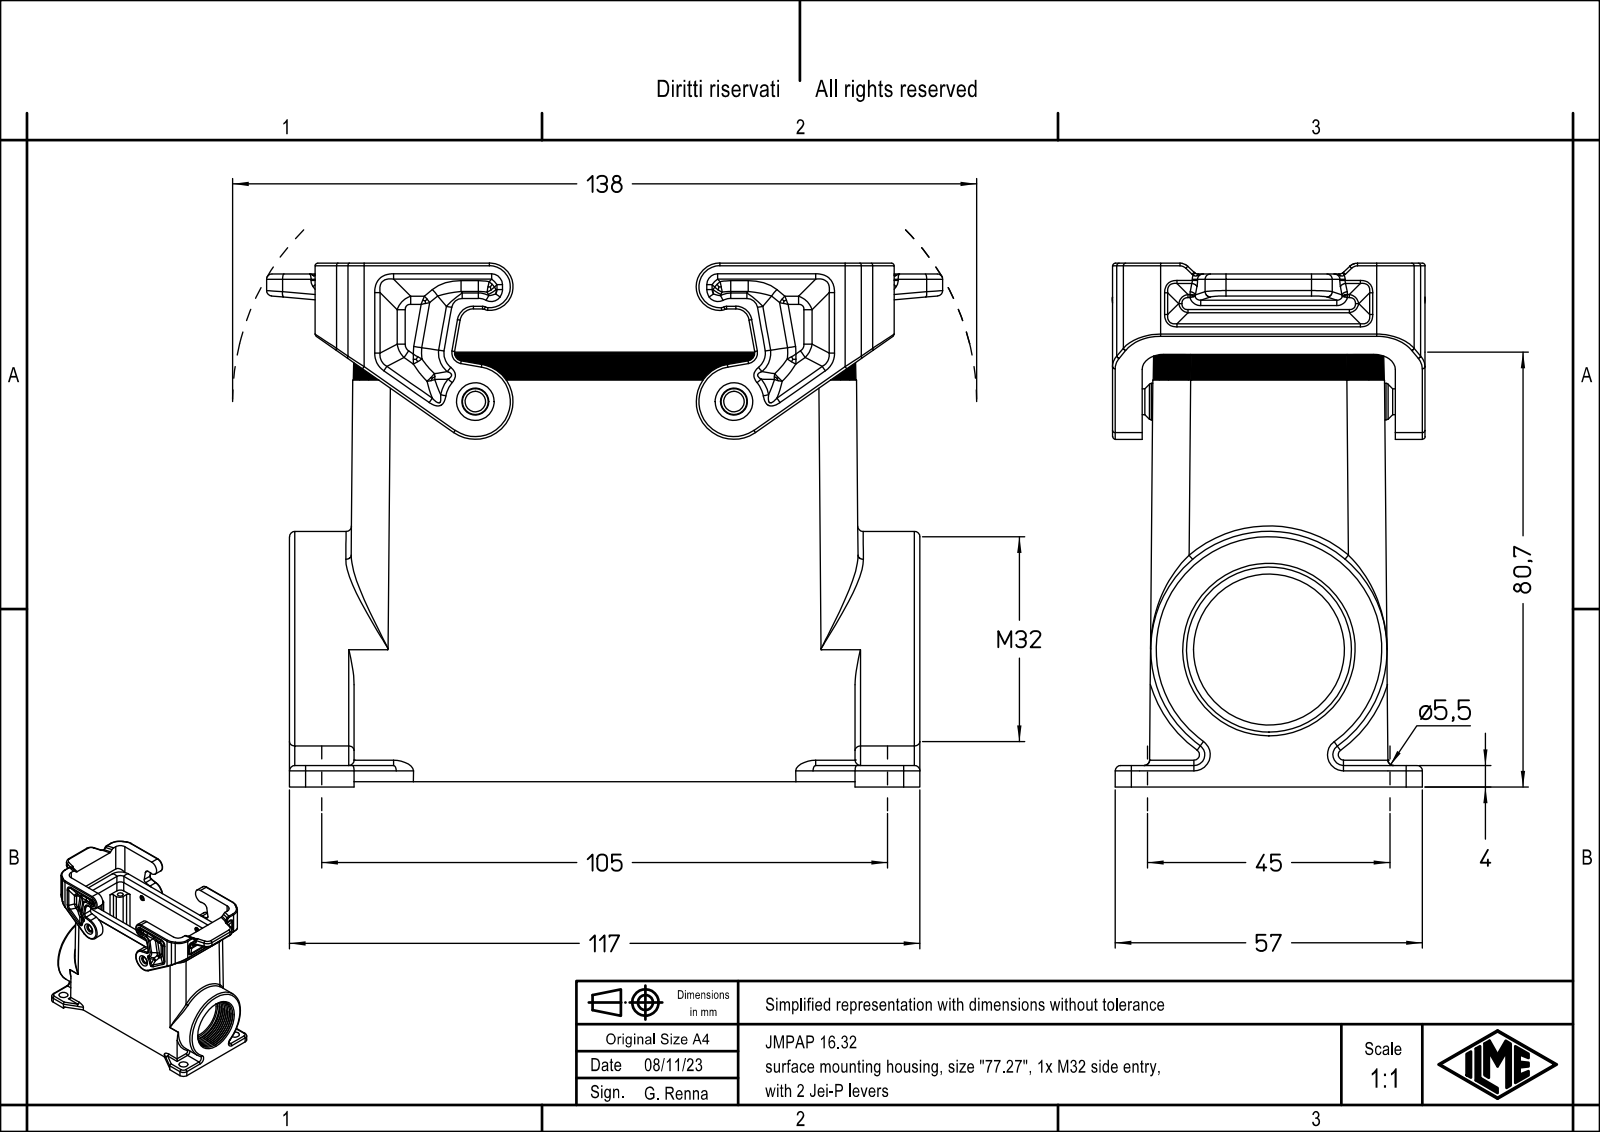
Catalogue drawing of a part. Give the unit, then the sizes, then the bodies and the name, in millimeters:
Units: millimetres
Overall size (bounding box): 125.5 × 97.2 × 58.08
Round holes (diameter × count): ⌀3 ×4, ⌀3.5 ×4, ⌀5.5 ×3, ⌀4.8 ×2, ⌀28 ×1, ⌀30.6 ×1
Round bosses / shafts (diameter × count): ⌀6.8 ×2, ⌀43.87 ×1
Partial cylindrical surfaces — rounded edges, fillets, slot ends (radius × count): R0.5 ×50, R1 ×44, R3 ×38, R2 ×26, R1.5 ×12, R4 ×12, R6 ×12, R7 ×10
Main face-to-face distances: 3, 1, 4, 47, 107.25, 9.75, 2, 7, 5.5, 52.5
Hole centre spacings: 16.43, 38.54, 91.69, 98.09, 27, 77.5, 82.07, 45
Volume: 158 531 mm³ · Surface area: 67 956 mm²
Bodies: 1 solid, 867 faces (173 planar, 312 cylindrical, 382 other)
Part name (STEP PRODUCT): JMPAP 16.32
STEP written by: Creo Elements/Direct Modeling 20.1B 02-Apr-2019 (C) Parametric Technology GmbH (AUTOMOTIVE_DESIGN)
